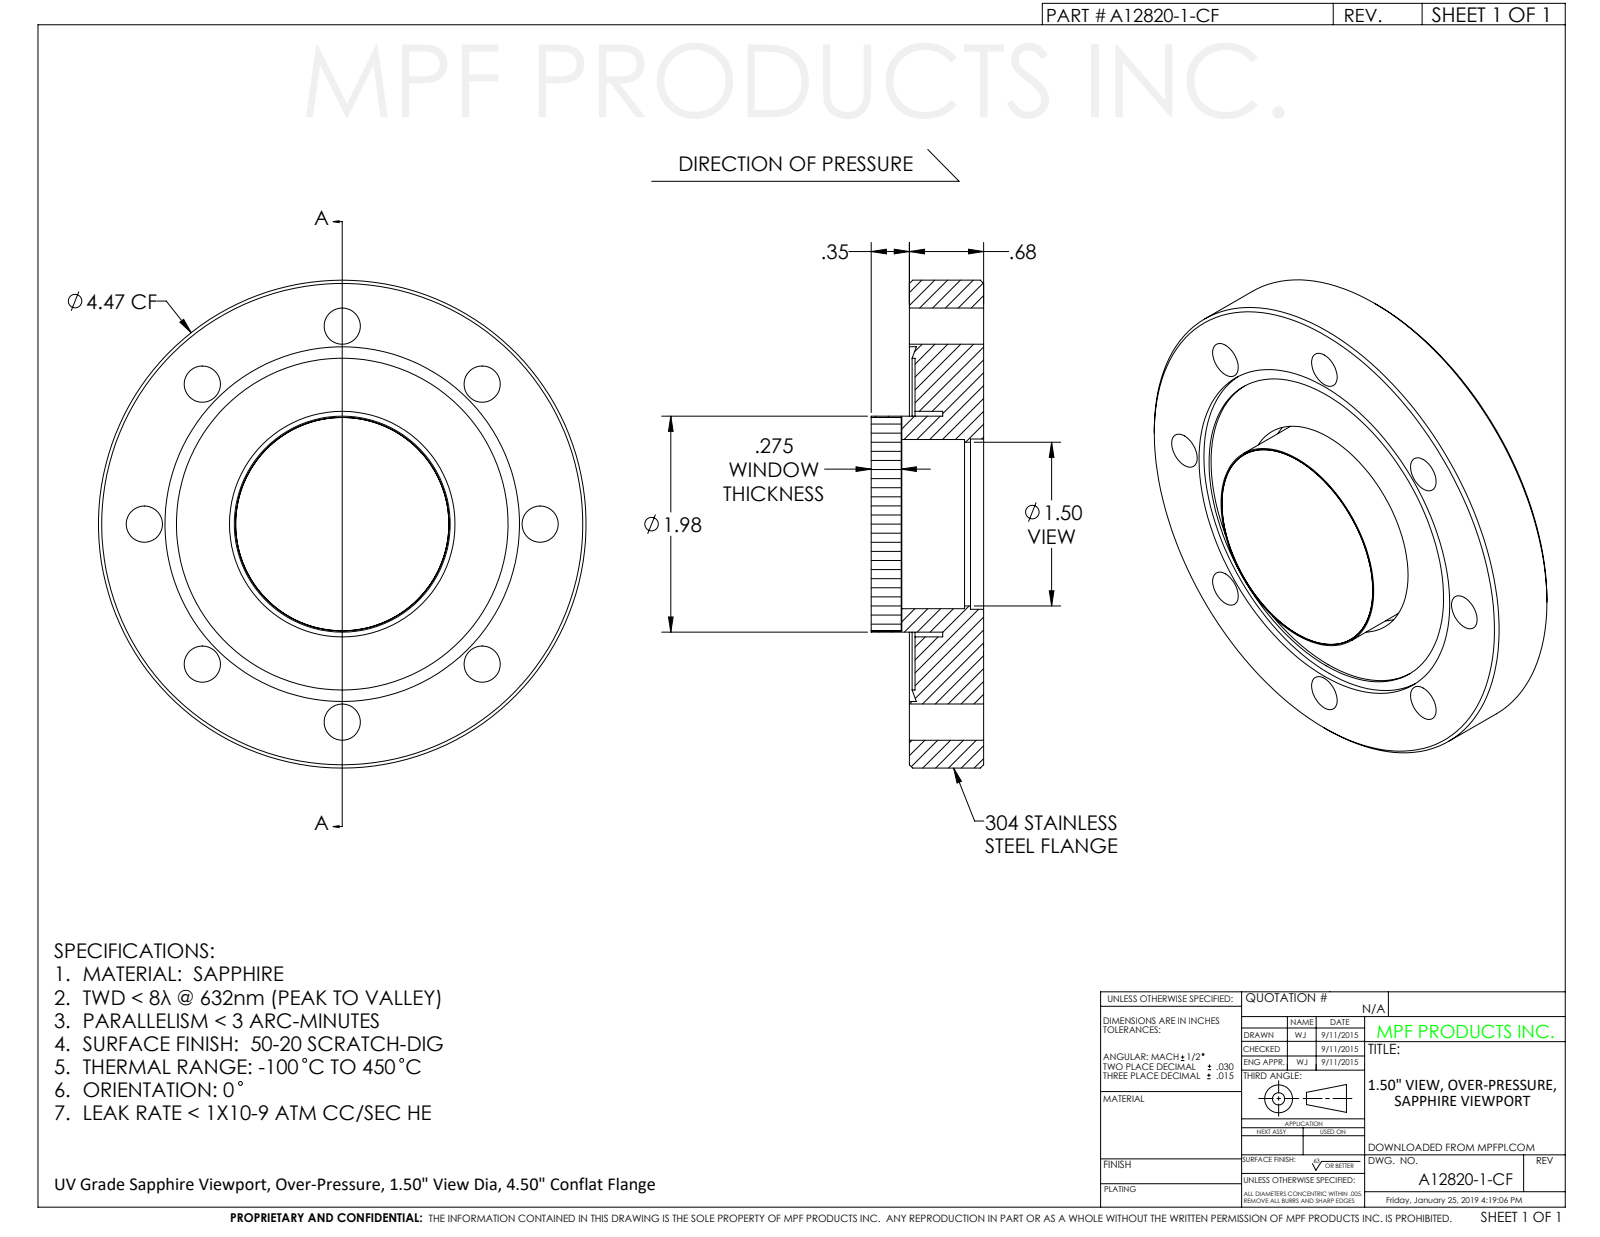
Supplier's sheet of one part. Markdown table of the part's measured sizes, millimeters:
| quantity | value |
| --- | --- |
| part name | A12820-1 |
| STEP written by | SolidWorks 2018 (CONFIG_CONTROL_DESIGN) |
| units | millimeters |
| bodies | 2 solids, 224 faces (139 planar, 36 cylindrical, 49 other) |
| overall size | 113.5 × 113.5 × 26.2 |
| volume | 155 800 mm³ |
| surface area | 39 320 mm² |
| round holes (diameter × count) | 8.4 × 8, 38.1 × 1, 39.4 × 1, 39.6 × 1, 49.7 × 1, 52.5 × 1, 77.2 × 1, 82.6 × 1 |
| round bosses / shafts (diameter × count) | 113.5 × 1, 50.3 × 1 |
| main face-to-face distances | 17.3, 16, 1.3, 26.2, 10.2, 8.9, 19.2, 3.2, 1.9, 7 |
| hole center spacings | 35.3, 46.1, 85.1, 65.2, 65.2, 92.2, 92.2 |
